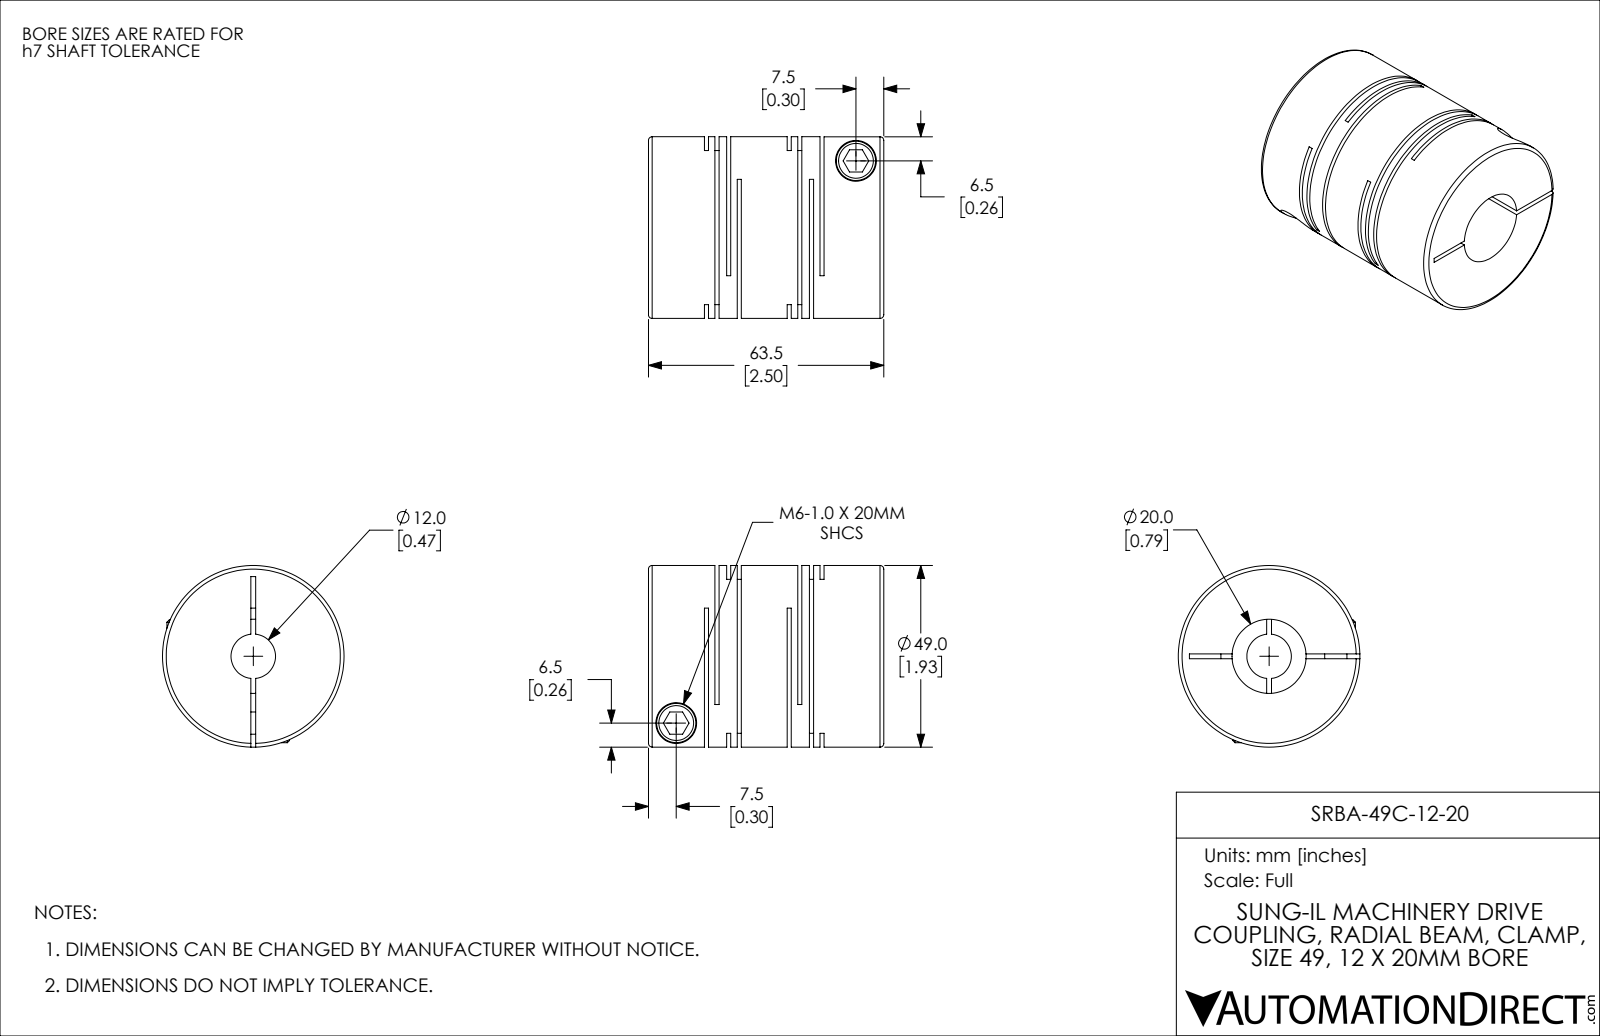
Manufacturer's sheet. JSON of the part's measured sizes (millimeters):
{"part_name": "SRBA-49C-12-20", "step_written_by": "SolidWorks 2021 (CONFIG_CONTROL_DESIGN)", "units": "millimeters", "bodies": {"solids": 1, "faces": 114, "planar": 60, "cylindrical": 42, "other": 12}, "overall_size": [63.5, 49, 49], "volume_mm3": 89108, "surface_area_mm2": 38213, "round_holes": [[6, 2], [11, 2], [12, 1], [20, 1]], "round_bosses_or_shafts": [[10.6, 2], [49, 1]], "face_to_face_distances": [6, 1.1, 2.85, 22.35, 1.75, 4.9, 21.25, 3.15, 19.5, 16.35]}
